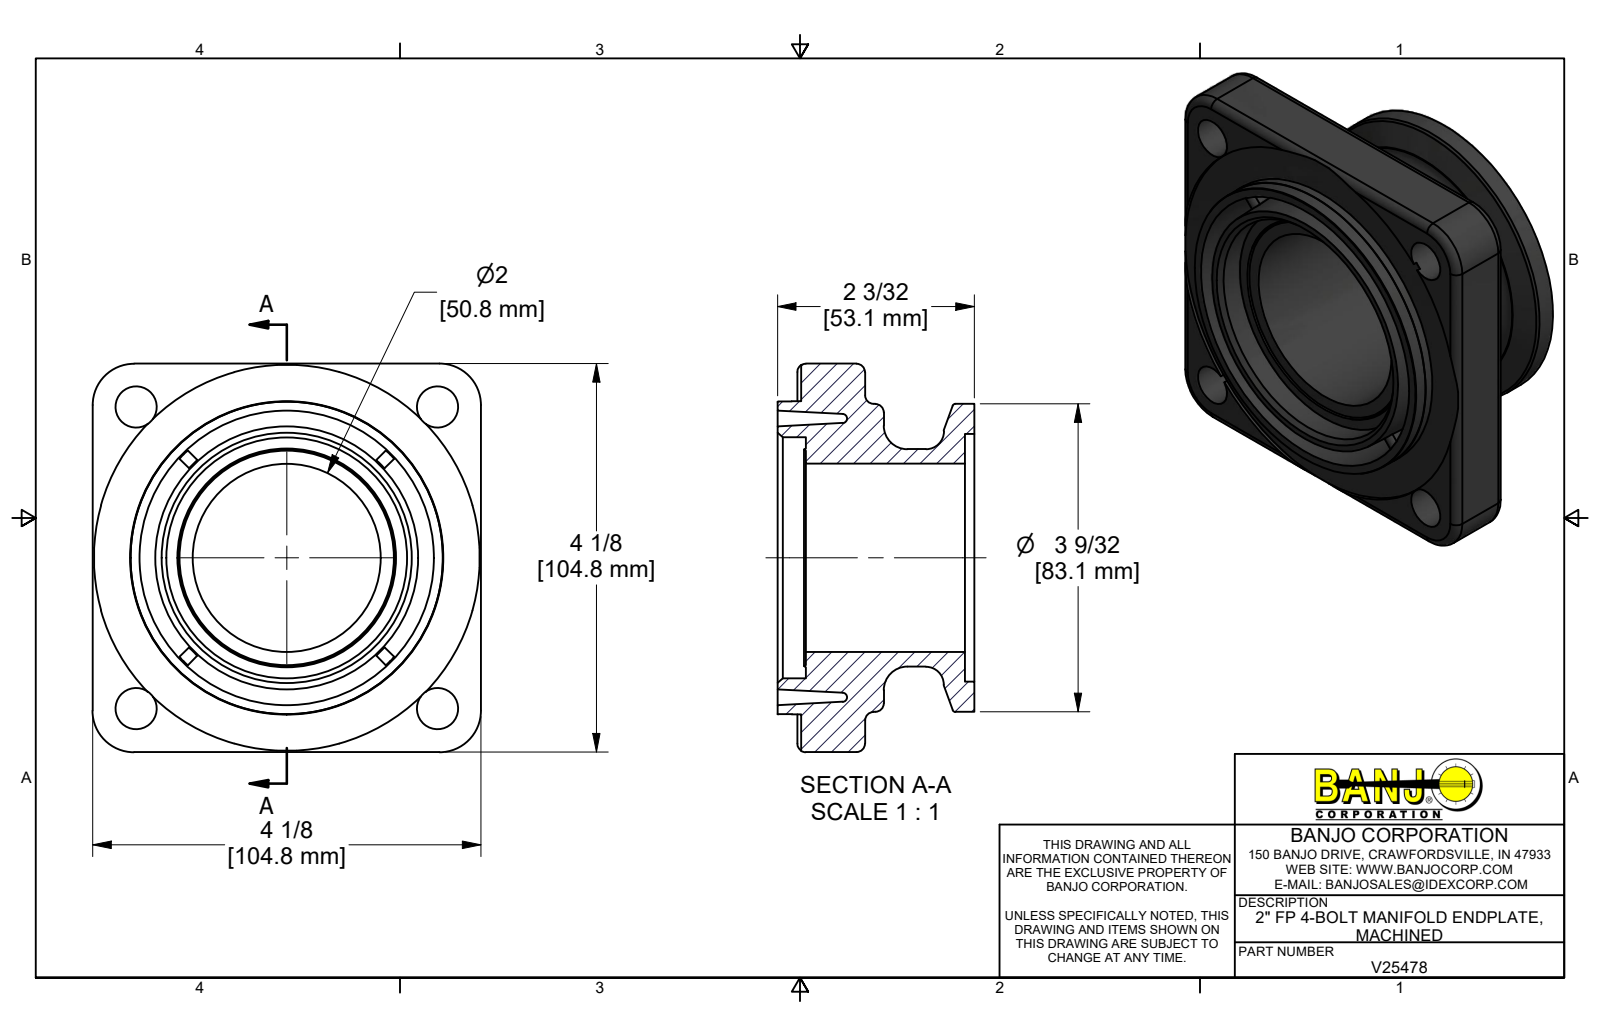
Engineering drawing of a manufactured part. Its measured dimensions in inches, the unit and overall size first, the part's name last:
Units: inches
Overall size (bounding box): 4.125 × 4.125 × 2.09
Round holes (diameter × count): ⌀0.438 ×4, ⌀2 ×1, ⌀2.56 ×1, ⌀2.63 ×1, ⌀4.1 ×1
Round bosses / shafts (diameter × count): ⌀3.325 ×1, ⌀3.32 ×1, ⌀3.27 ×1, ⌀2.31 ×1
Partial cylindrical surfaces — rounded edges, fillets, slot ends (radius × count): R0.09 ×8, R0.062 ×4, R0.44 ×4
Main face-to-face distances: 0.68, 4.125, 1.84, 1.16, 0.1, 1.74, 1.06, 0.04, 0.72, 1.78
Hole centre spacings: 2.265, 3.204, 4.531
Volume: 12.12 in³ · Surface area: 85.07 in²
Bodies: 1 solid, 87 faces (27 planar, 36 cylindrical, 24 other)
Part name (STEP PRODUCT): V25478; V25378X
STEP written by: Autodesk Inventor 2019 (AUTOMOTIVE_DESIGN)
